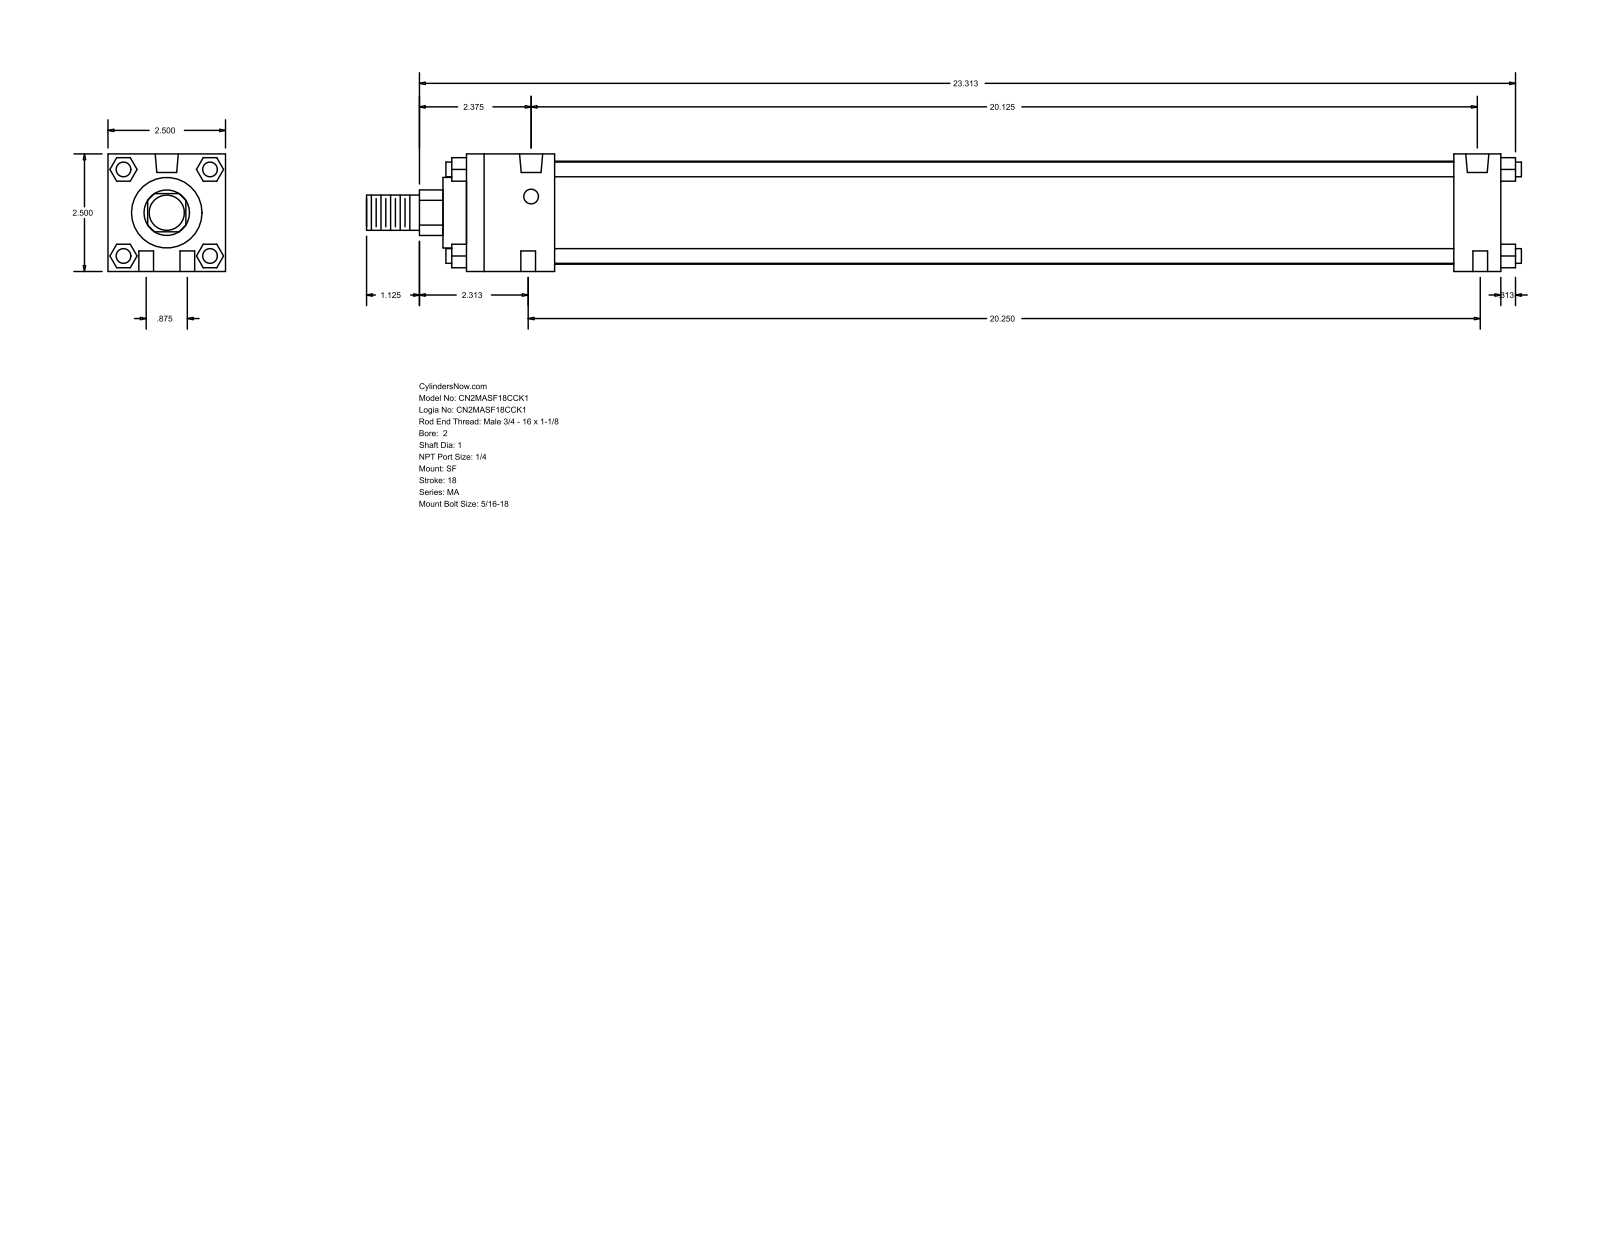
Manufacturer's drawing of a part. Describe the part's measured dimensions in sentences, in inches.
The part is named "MA_SF__0200_1". Its 3-D file was written by "GSSL Pune (CONFIG_CONTROL_DESIGN)". It is 0 solids with 124 faces: 94 planar, 30 cylindrical and 0 other. Overall it measures 24.563 by 2.5 by 2.5 inches. Round holes: 6 of diameter 0.313, 2 of diameter 0.492. Round bosses or shafts: 4 of diameter 0.313, 1 of diameter 2.19, 1 of diameter 1.5, 1 of diameter 1, 1 of diameter 0.75. Partial cylindrical surfaces (rounded edges, fillets, slot ends): 1 of radius 0.484. The main face-to-face distances are 2.5, 22, 0.5, 1, 21, 1.875, 19.125, 20.125, 1.593, 0.92. The hole center spacings are 0.442, 20.192, 0.875, 20.125, 20.25, 20.269.
